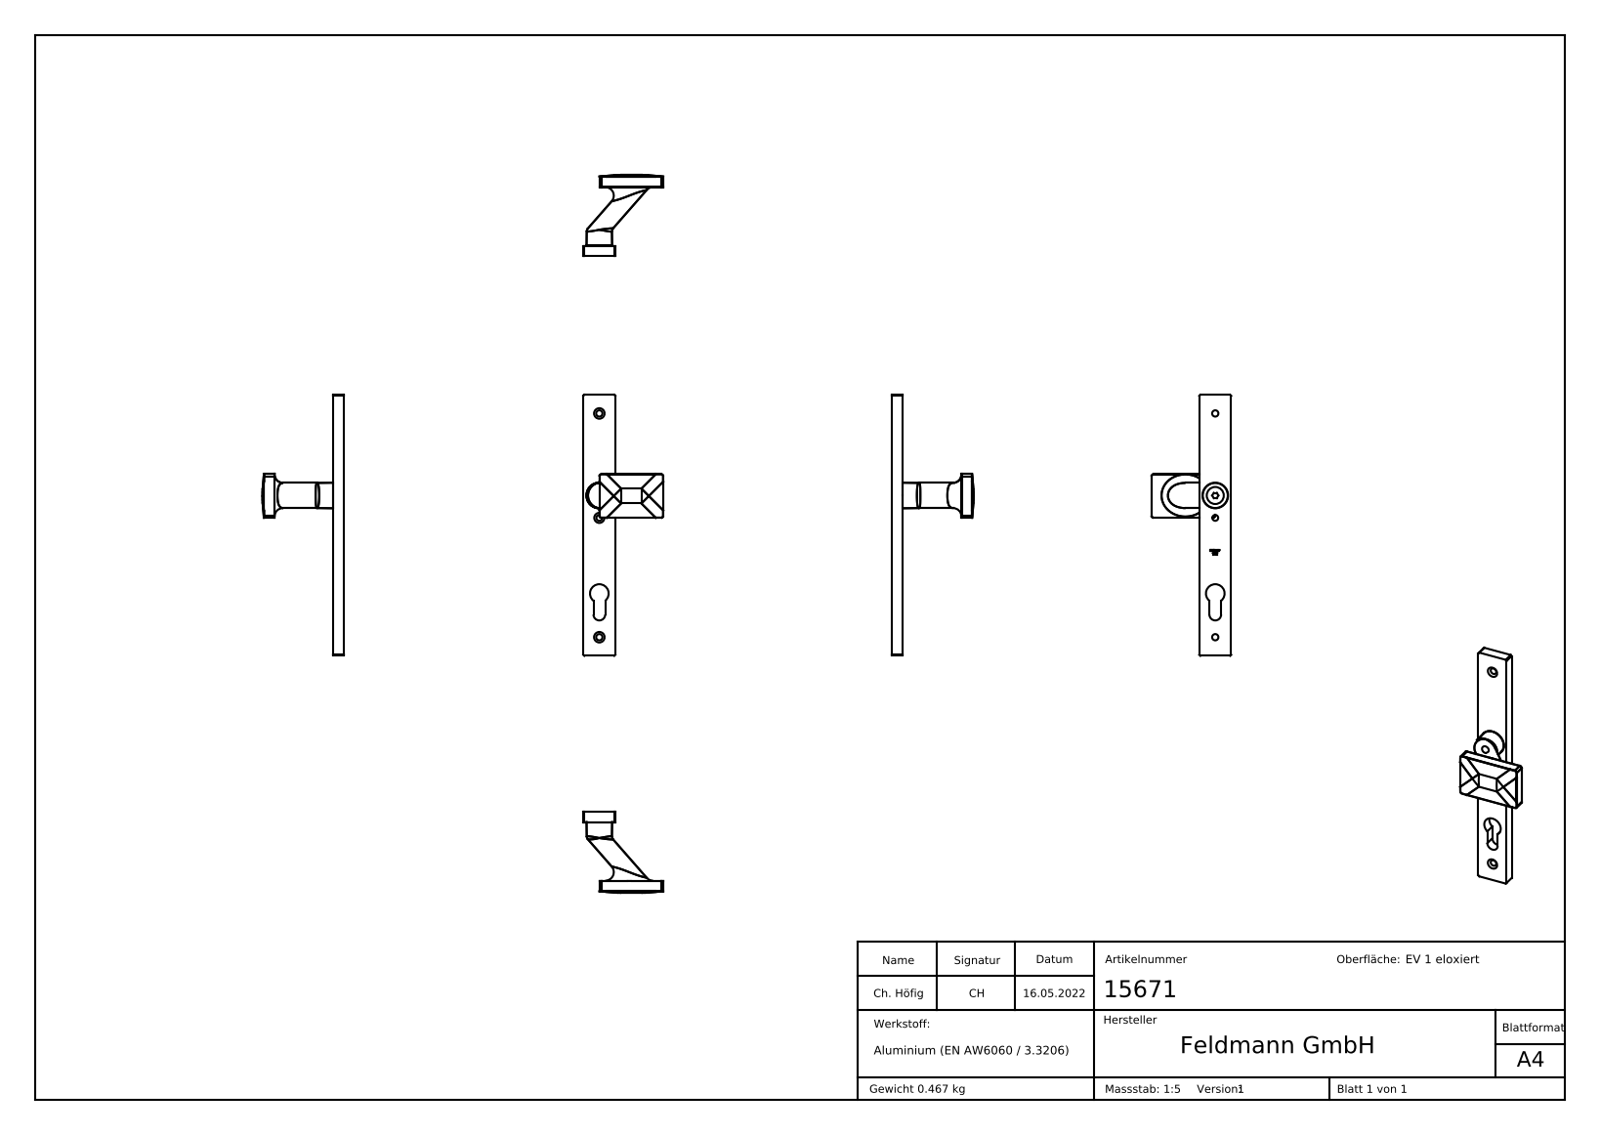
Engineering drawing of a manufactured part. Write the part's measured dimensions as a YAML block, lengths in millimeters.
part_name: "15671 Teil 2_15671 Teil2 Keyshot; 15671; DIN 7991 Konfig_M8x20 Keyshot; 15671 Teil 3_15671 Teil1a Keyshot (+1 more)"
step_written_by: "SolidWorks 2018 (CONFIG_CONTROL_DESIGN)"
units: millimeters
bodies: {solids: 4, faces: 187, planar: 34, cylindrical: 75, other: 78}
overall_size: [245, 80, 76.49]
volume: 117786
surface_area: 34464
round_holes:
  - {diameter: 5.9, count: 2}
  - {diameter: 5.5, count: 1}
  - {diameter: 6.8, count: 1}
  - {diameter: 13, count: 1}
  - {diameter: 20, count: 1}
  - {diameter: 24, count: 1}
round_bosses_or_shafts:
  - {diameter: 23.5, count: 1}
  - {diameter: 16, count: 1}
  - {diameter: 8, count: 1}
partial_cylinders:
  - {radius: 0.1, count: 28}
  - {radius: 0.3, count: 8}
  - {radius: 80, count: 5}
  - {radius: 2, count: 4}
  - {radius: 5.5, count: 1}
  - {radius: 8.75, count: 1}
face_to_face_distances: [10, 30, 65, 55, 5, 60, 41, 20, 80, 50]
hole_center_spacings: [21, 77, 98, 112, 133, 210]
